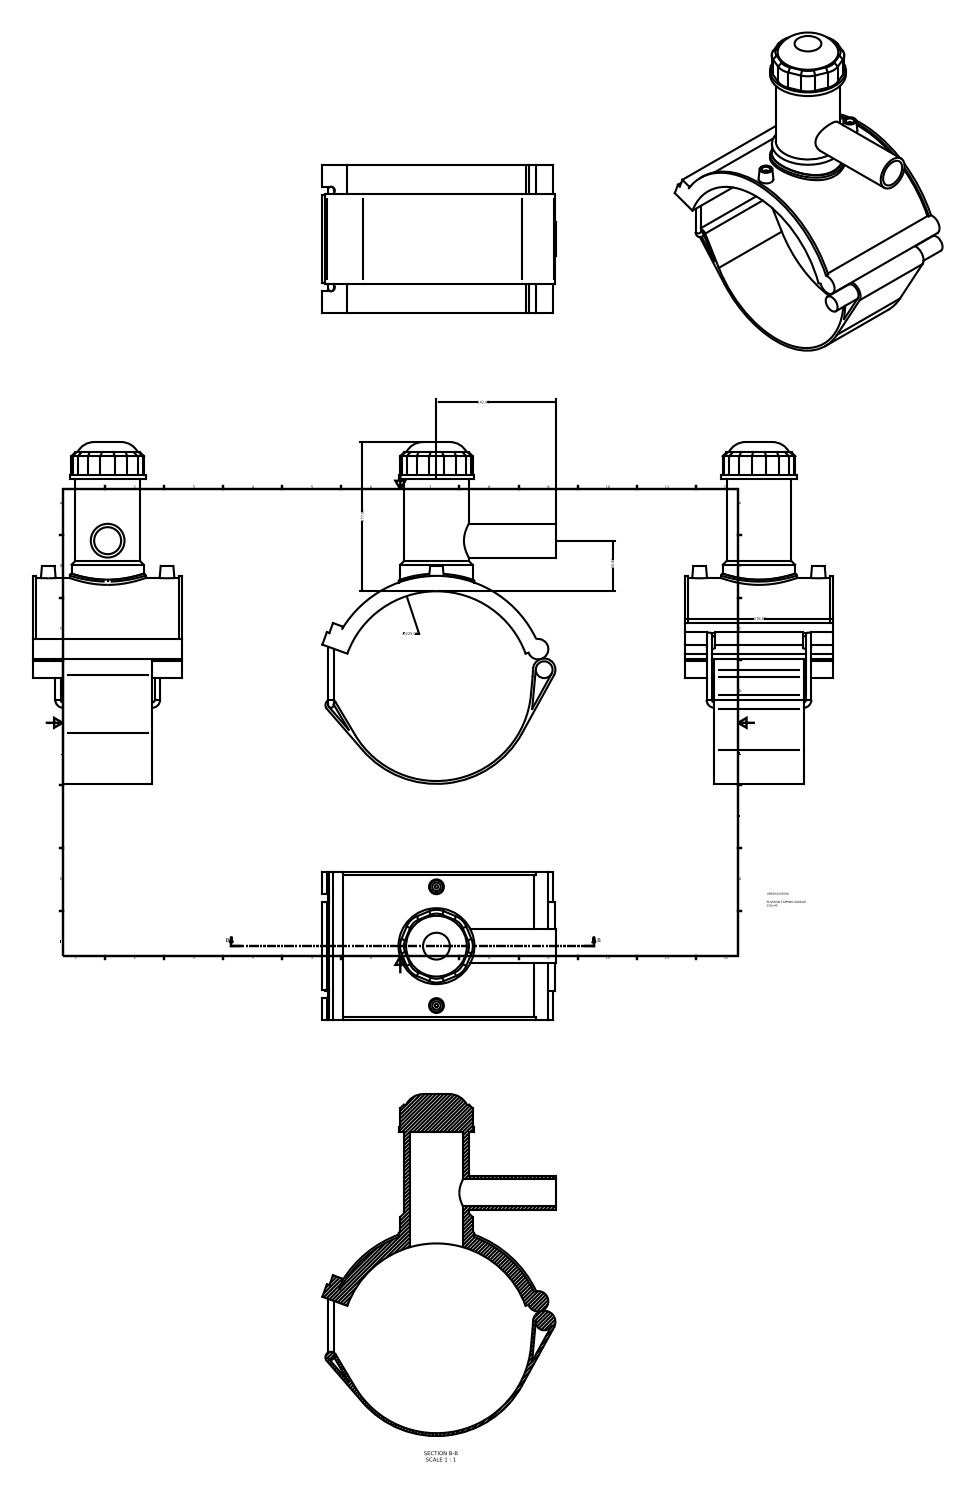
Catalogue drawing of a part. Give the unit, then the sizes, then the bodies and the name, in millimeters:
Units: millimetres
Overall size (bounding box): 405.38 × 277.32 × 176
Round holes (diameter × count): ⌀10 ×2, ⌀32 ×1, ⌀63 ×1
Round bosses / shafts (diameter × count): ⌀6.3 ×2, ⌀4 ×2, ⌀90 ×1, ⌀85.5 ×1, ⌀76.5 ×1, ⌀40 ×1, ⌀19.9 ×1
Partial cylindrical surfaces — rounded edges, fillets, slot ends (radius × count): R22.5 ×8, R4.72 ×2, R112.5 ×2, R3.15 ×1, R6.53 ×1, R12.12 ×1, R13.33 ×1, R115.88 ×1
Main face-to-face distances: 176, 3.4, 3.38, 3.37, 35.2, 140.8, 3, 3.15, 28.35, 15.76
Hole centre spacings: 70.4, 140.8
Volume: 1 619 000 mm³ · Surface area: 349 914 mm²
Bodies: 1 solid, 121 faces (68 planar, 38 cylindrical, 15 other)
Part name (STEP PRODUCT): 496304225040
STEP written by: Autodesk Inventor 2015 (AUTOMOTIVE_DESIGN)
